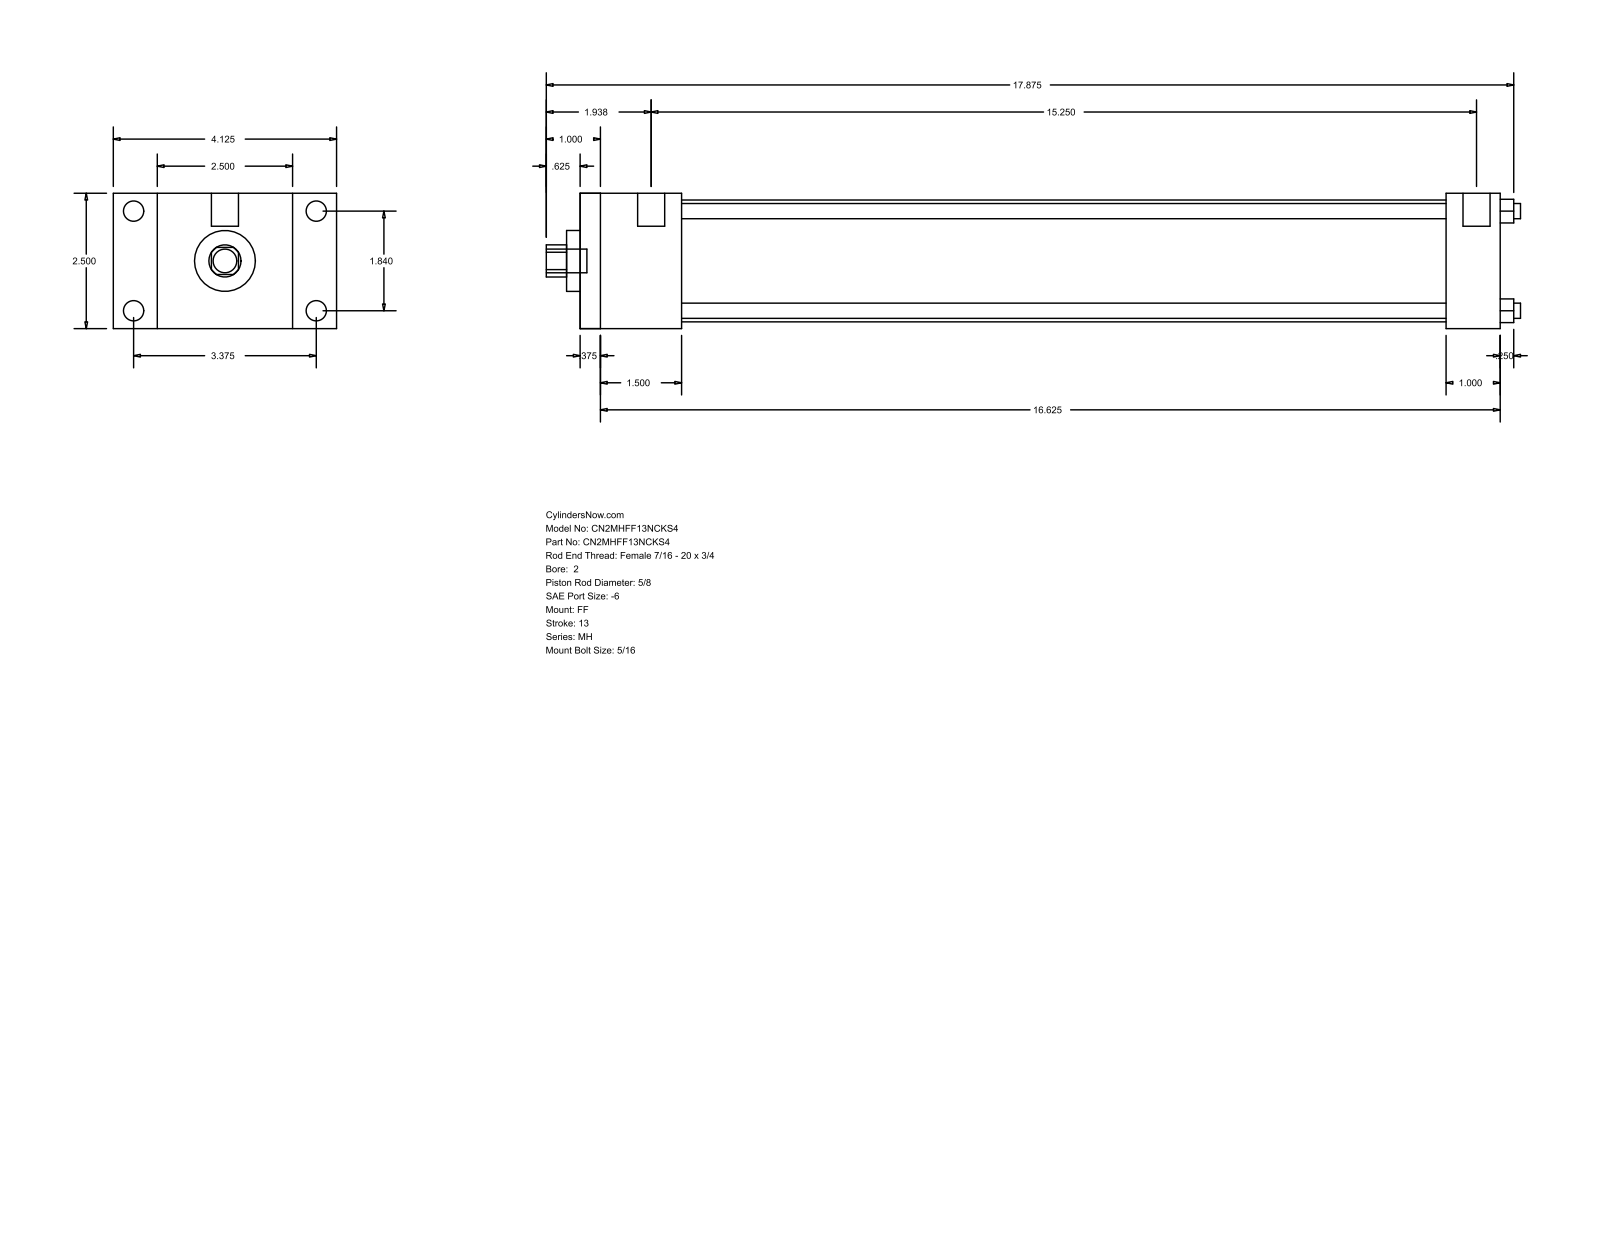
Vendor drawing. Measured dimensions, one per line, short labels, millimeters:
name: MH_FF__0200_0.625
written by: GSSL Pune (CONFIG_CONTROL_DESIGN)
unit: mm
bodies: 0 solids, 92 faces (64 planar, 28 cylindrical, 0 other)
size: 457.2 × 104.78 × 63.5
holes: 4× ⌀7.14, 1× ⌀15.88, 1× ⌀28.57, 1× ⌀57.15
bosses: 4× ⌀9.53, 4× ⌀5.56, 2× ⌀12.7, 1× ⌀11.11
rounds: 1× R7.54
face distances: 63.5, 431.8, 9.52, 422.28, 38.1, 47.62, 406.39, 396.87, 358.77, 384.18
hole spacings: 33.05, 46.74, 66.1
